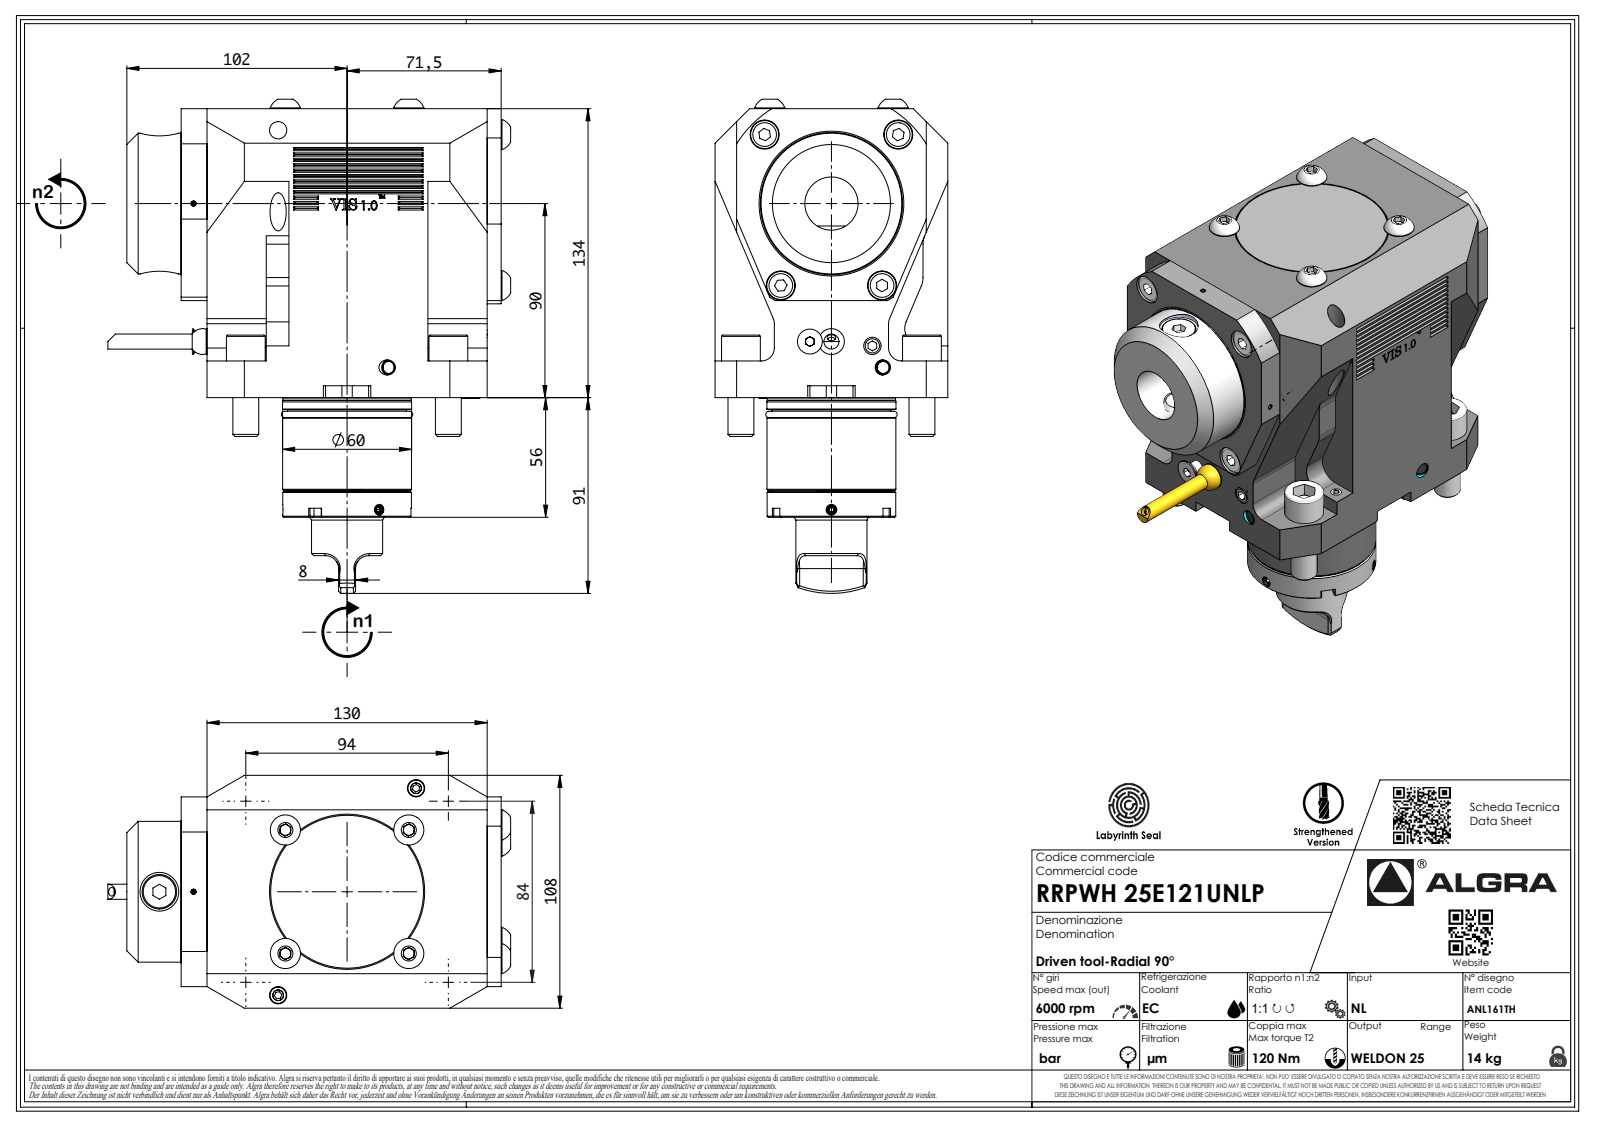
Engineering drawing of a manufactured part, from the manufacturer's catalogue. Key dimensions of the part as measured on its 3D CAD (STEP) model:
Part name (STEP PRODUCT): RRPWH25E121UNLP
STEP written by: SolidWorks 2023 (AUTOMOTIVE_DESIGN)
Units: millimetres
Bodies: 1 solid, 916 faces (638 planar, 110 cylindrical, 168 other)
Overall size (bounding box): 224.8 × 173.7 × 108
Volume: 2 056 000 mm³ · Surface area: 125 185 mm²
Round holes (diameter × count): ⌀2.1 ×1
Round bosses / shafts (diameter × count): ⌀18 ×4, ⌀12 ×4, ⌀65.3 ×1, ⌀59.9 ×1, ⌀59.8 ×1, ⌀59.7 ×1, ⌀59.5 ×1, ⌀55.2 ×1
Partial cylindrical surfaces — rounded edges, fillets, slot ends (radius × count): R0.2 ×21, R8 ×18, R6 ×10, R0.33 ×7, R0.52 ×7, R3.7 ×7, R10 ×4, R3 ×3
Main face-to-face distances: 134, 108, 27.5, 12, 102.5, 148.5, 6.5, 136.5, 5.5, 39.5
